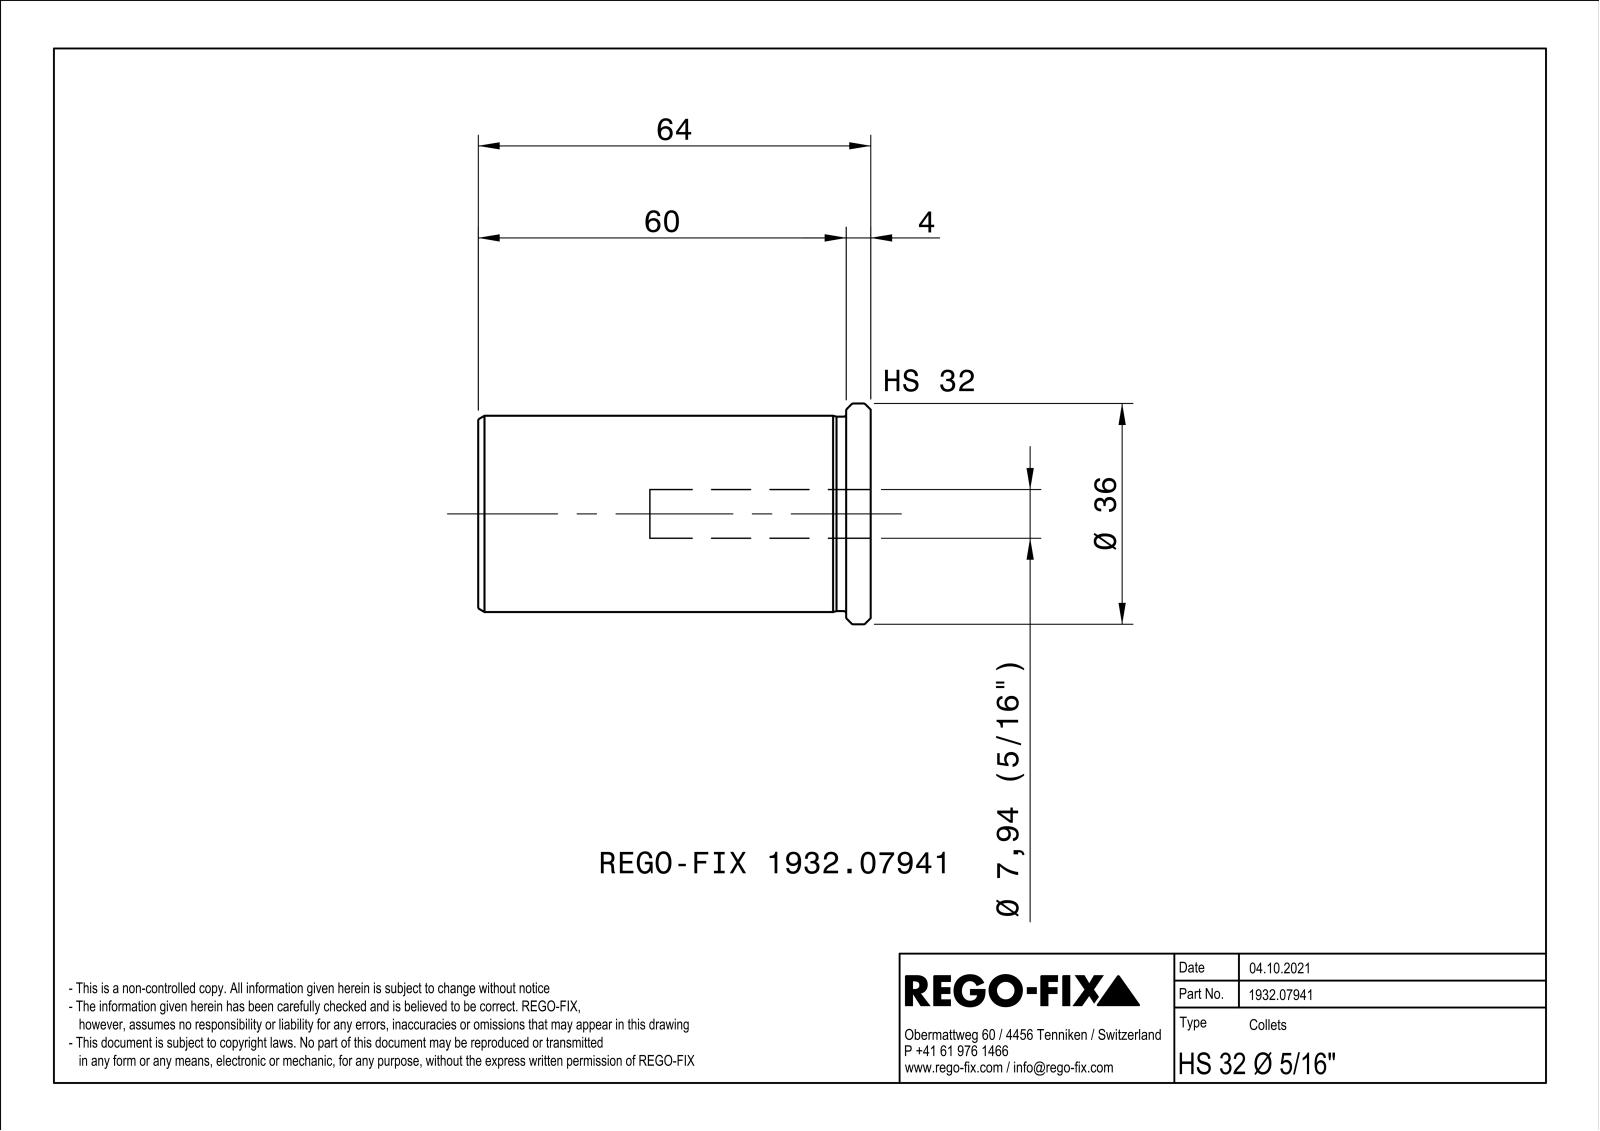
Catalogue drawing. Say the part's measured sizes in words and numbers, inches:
The part is named "NOCUT". Its 3-D file was written by "SIEMENS PLM Software Solid Edge ST10 (AUTOMOTIVE_DESIGN)". It is 1 solid with 72 faces: 22 planar, 12 cylindrical and 38 other. Overall it measures 2.52 by 1.417 by 1.417 inches. Its volume is 2.377 cubic inches and its surface area 22.04 square inches. Round holes: 1 of diameter 0.313, 1 of diameter 0.394, 1 of diameter 1.043. Round bosses or shafts: 1 of diameter 1.417, 1 of diameter 1.26, 1 of diameter 1.248. The main face-to-face distances are 0.039, 2.52, 0.157, 2.362.
